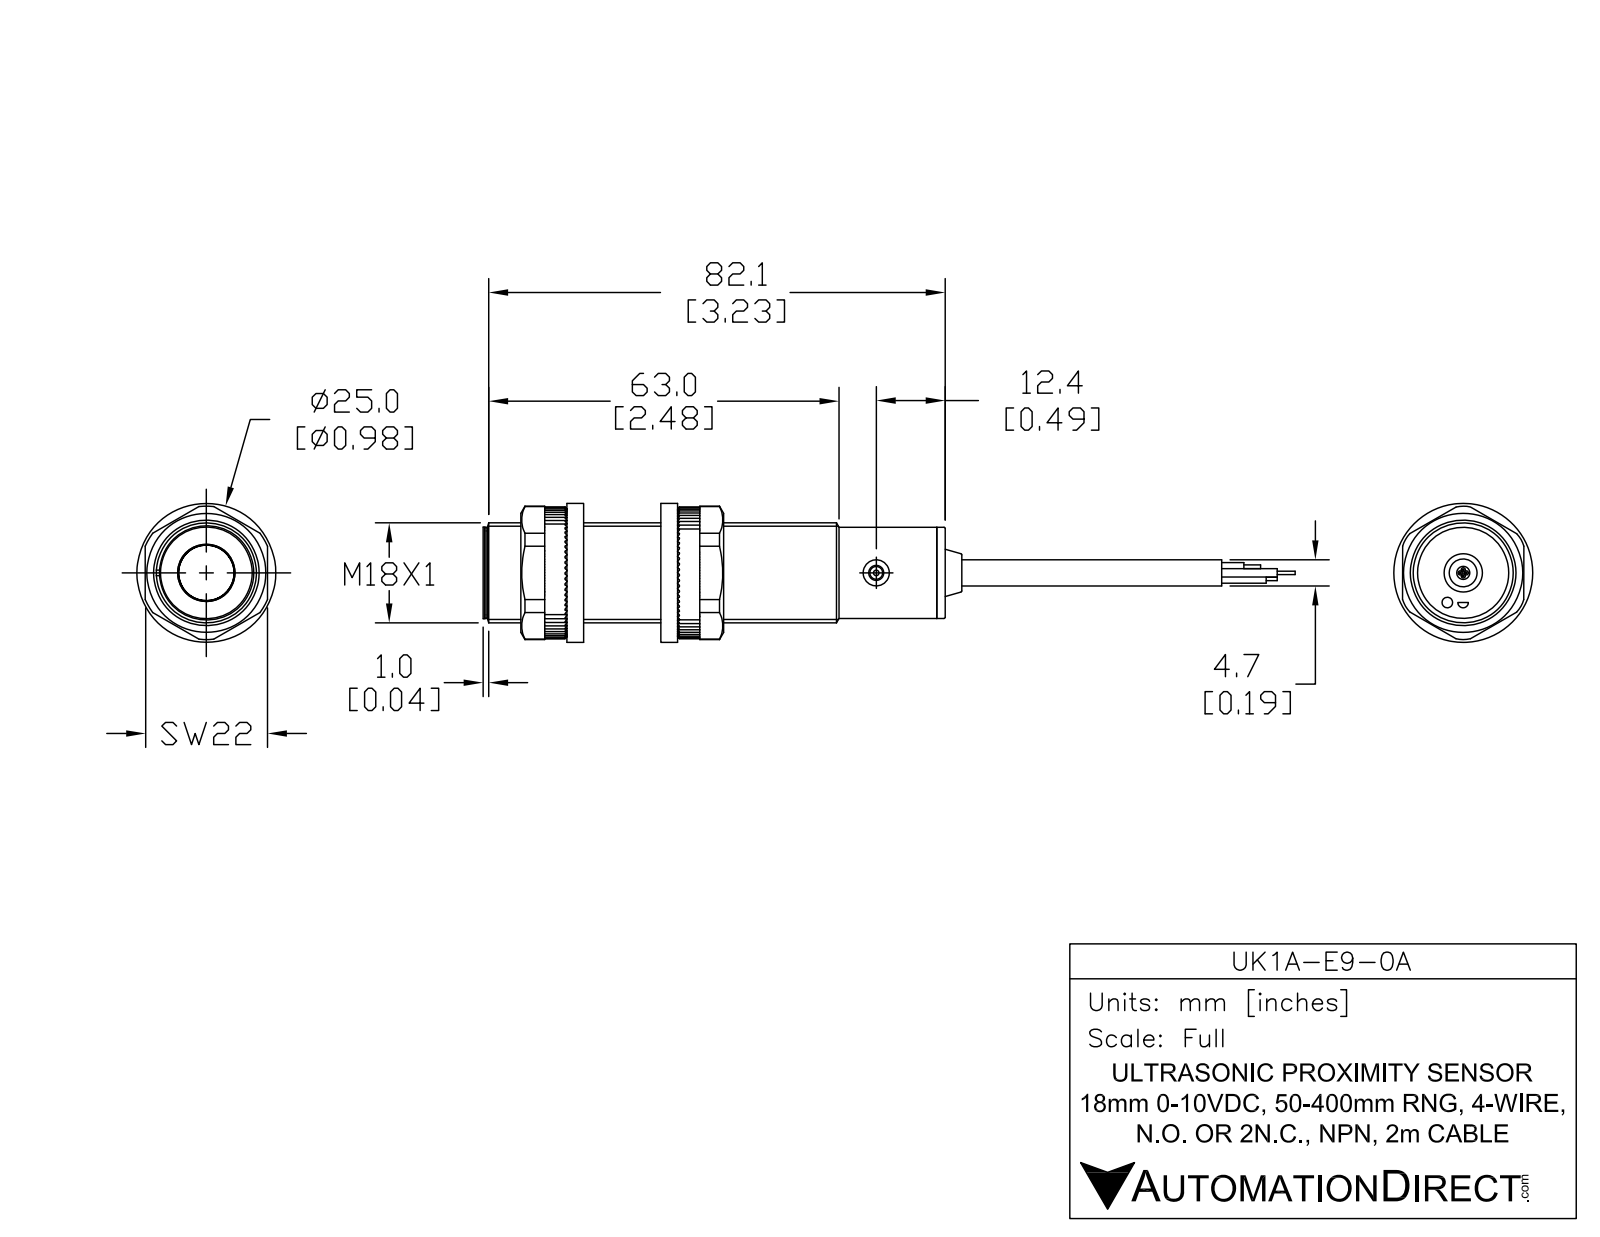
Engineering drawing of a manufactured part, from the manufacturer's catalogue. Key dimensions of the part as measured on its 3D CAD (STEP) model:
Part name (STEP PRODUCT): UK1A-E9-0A
STEP written by: SolidWorks 2017 (AUTOMOTIVE_DESIGN)
Units: inches
Bodies: 6 solids, 55 faces (17 planar, 24 cylindrical, 14 other)
Overall size (bounding box): 4.832 × 0.709 × 0.709
Volume: 1.285 in³ · Surface area: 10.69 in²
Round holes (diameter × count): ⌀0.185 ×2, ⌀0.106 ×1
Round bosses / shafts (diameter × count): ⌀0.709 ×1, ⌀0.646 ×1, ⌀0.622 ×1, ⌀0.374 ×1, ⌀0.189 ×1, ⌀0.091 ×1
Main face-to-face distances: 3.193, 3.252, 0.059, 0.039, 3.232, 3.291, 0.041, 3.234, 3.293, 3.257
